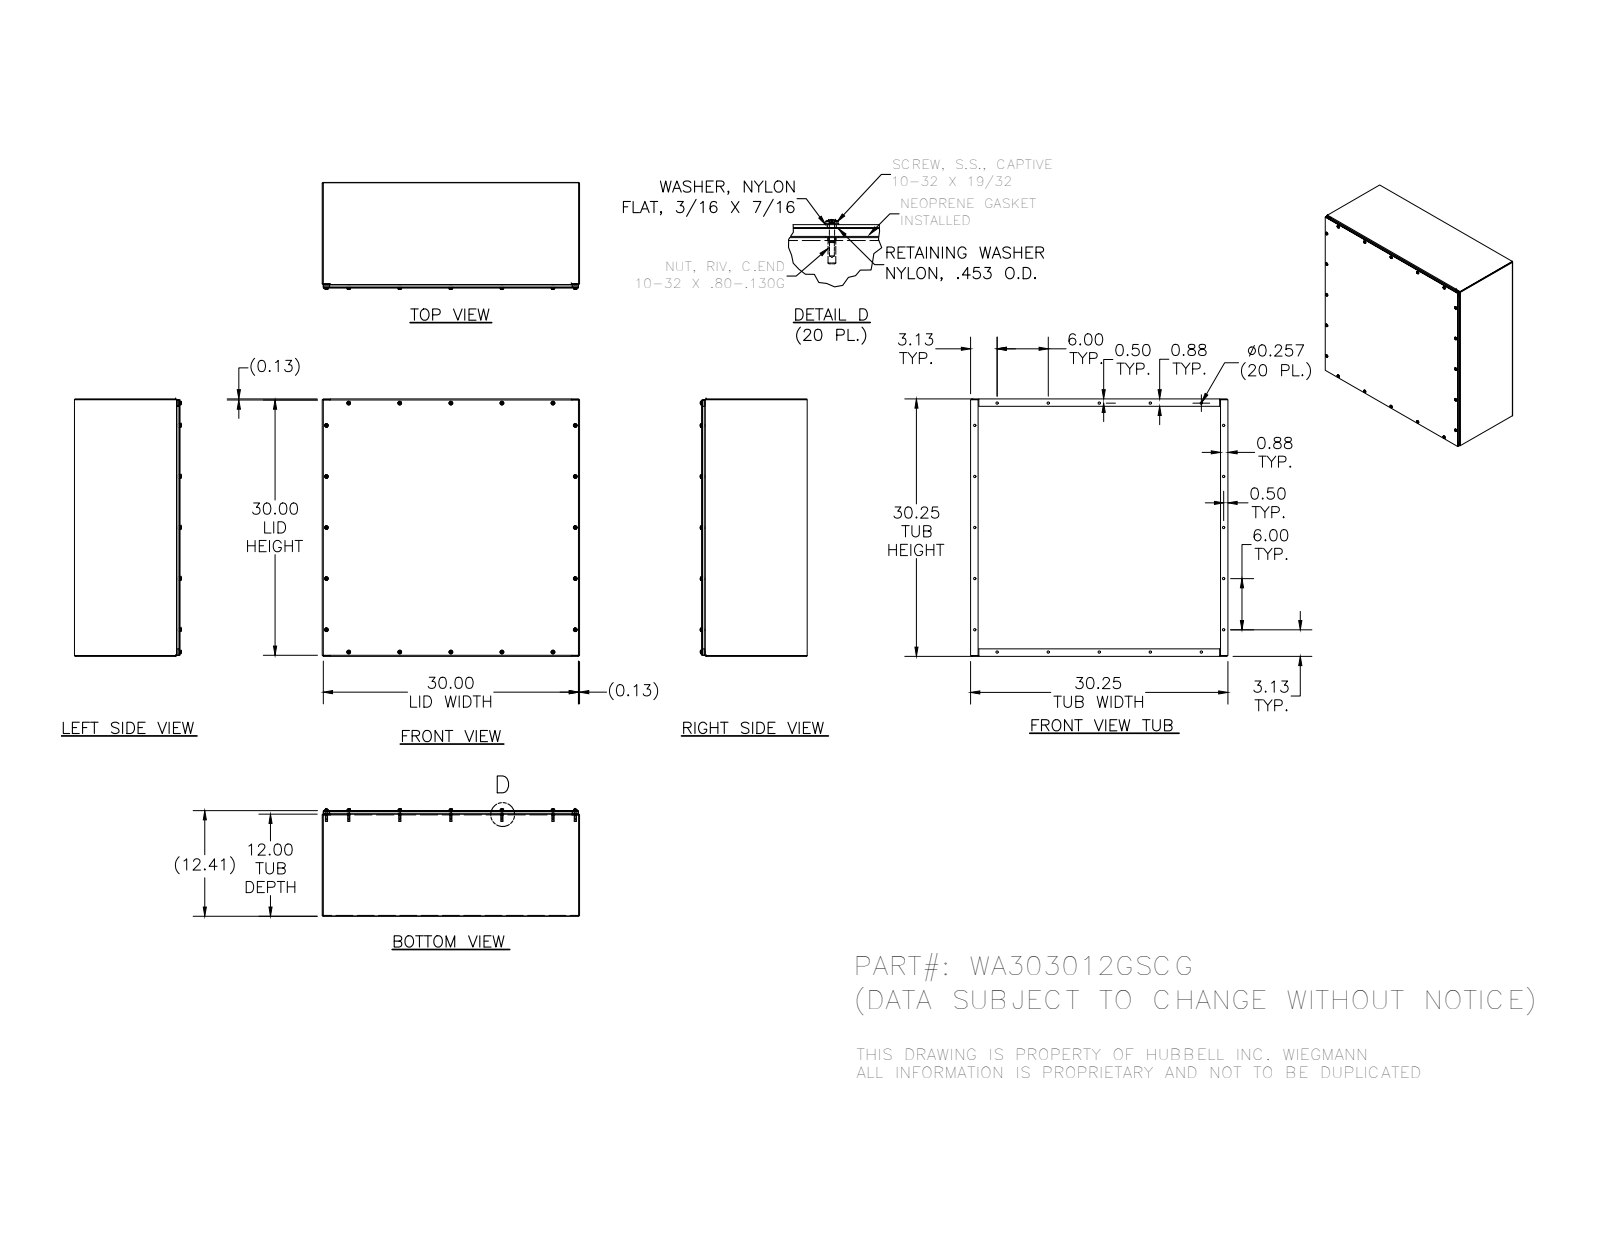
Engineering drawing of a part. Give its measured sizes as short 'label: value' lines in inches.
name: WA303012GSCG; 37210; 39077; WA3030GSCGLP (+5 more)
written by: SolidWorks 2014 (AUTOMOTIVE_DESIGN)
unit: in
bodies: 88 solids, 2020 faces (948 planar, 532 cylindrical, 540 other)
size: 30.25 × 30.25 × 12.568
volume: 335.8 in³; area: 6 998 in²
holes: 20× ⌀0.156, 20× ⌀0.188, 20× ⌀0.196, 20× ⌀0.257, 20× ⌀0.278, 20× ⌀0.281
bosses: 20× ⌀0.453, 20× ⌀0.437, 20× ⌀0.406, 20× ⌀0.248, 20× ⌀0.167
rounds: 20× R0.089, 6× R0.016, 6× R0.109
face distances: 0.094, 12.32, 30.156, 12.226, 12.414, 30.25, 30.062, 0.094, 30.156, 30.063
hole spacings: 6, 12, 29.859, 18, 31.616, 29.25, 34.345, 24
